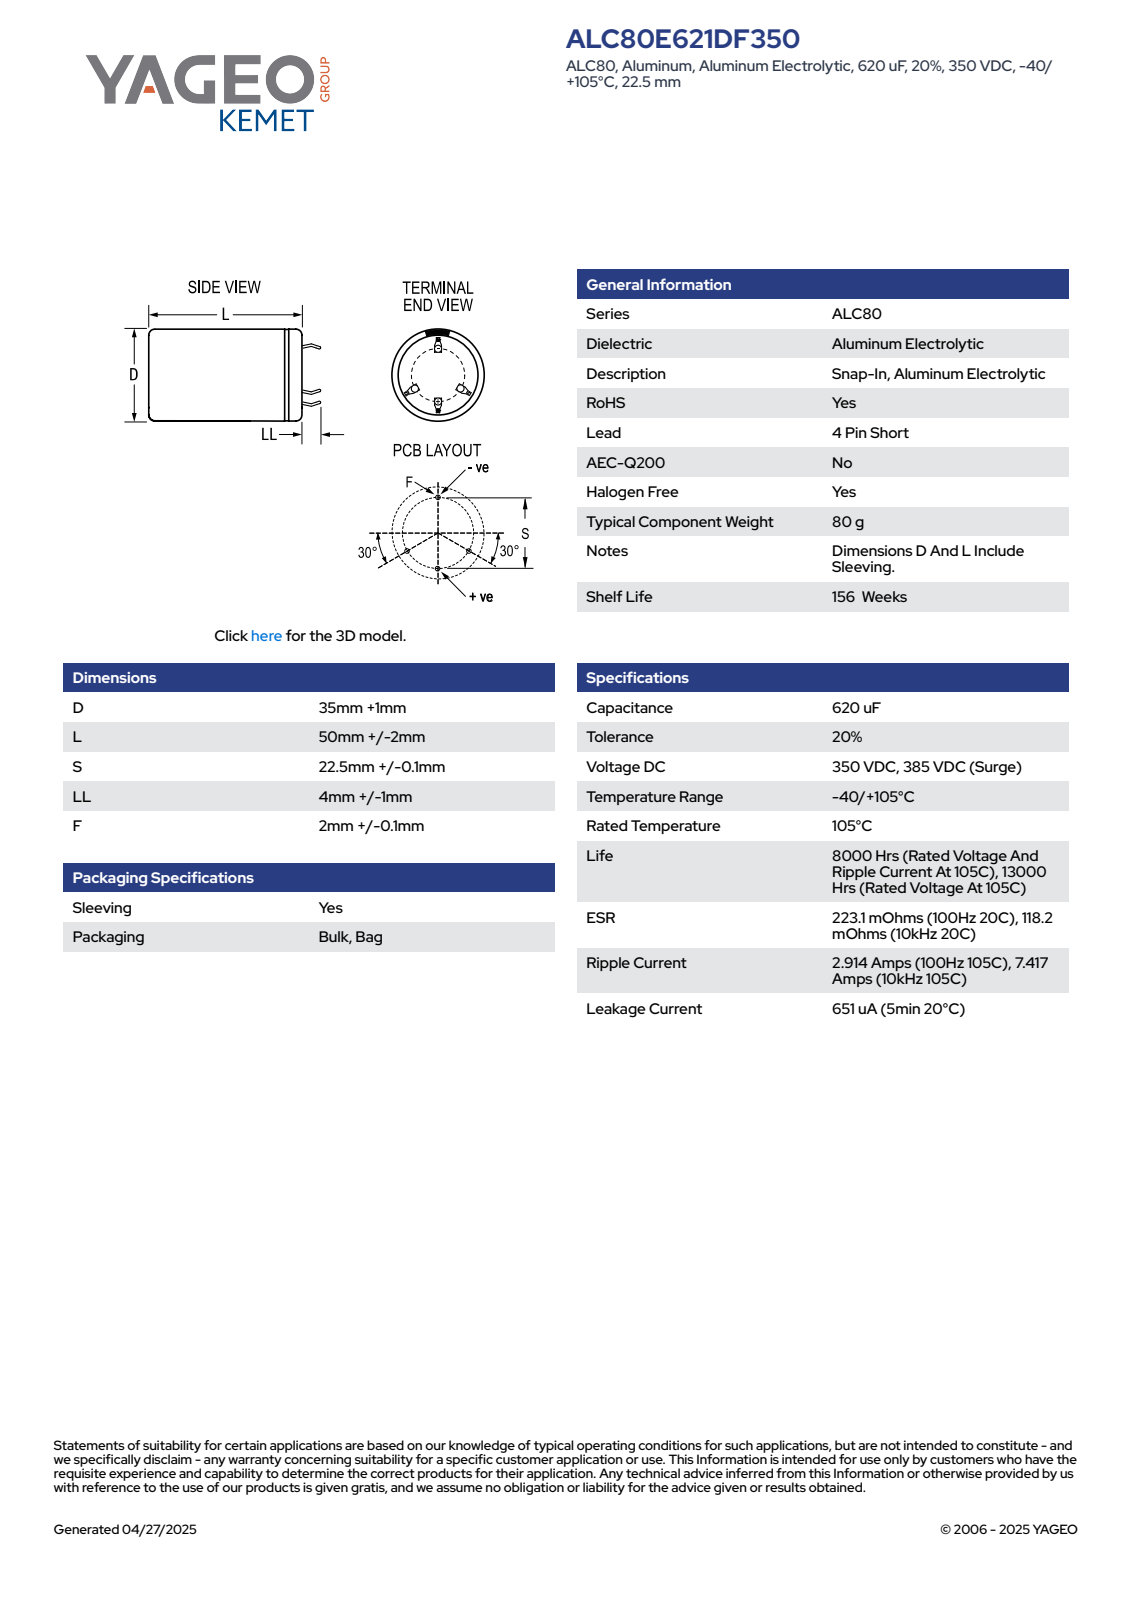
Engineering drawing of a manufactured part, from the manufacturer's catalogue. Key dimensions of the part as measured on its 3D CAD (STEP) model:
Part name (STEP PRODUCT): CARS_K4P_35X50_D36L52S22.5LL5F2.1
STEP written by: SolidWorks 2014 (AUTOMOTIVE_DESIGN)
Units: millimetres
Bodies: 1 solid, 134 faces (80 planar, 15 cylindrical, 39 other)
Overall size (bounding box): 56.99 × 36 × 36
Volume: 52 411 mm³ · Surface area: 7 941 mm²
Round holes (diameter × count): ⌀31.85 ×1
Round bosses / shafts (diameter × count): ⌀36 ×1
Partial cylindrical surfaces — rounded edges, fillets, slot ends (radius × count): R17.99 ×1
Main face-to-face distances: 51.99, 52.49, 0.5, 0.6, 0.75, 1.35, 0.51, 0.52, 2.1, 21.15
